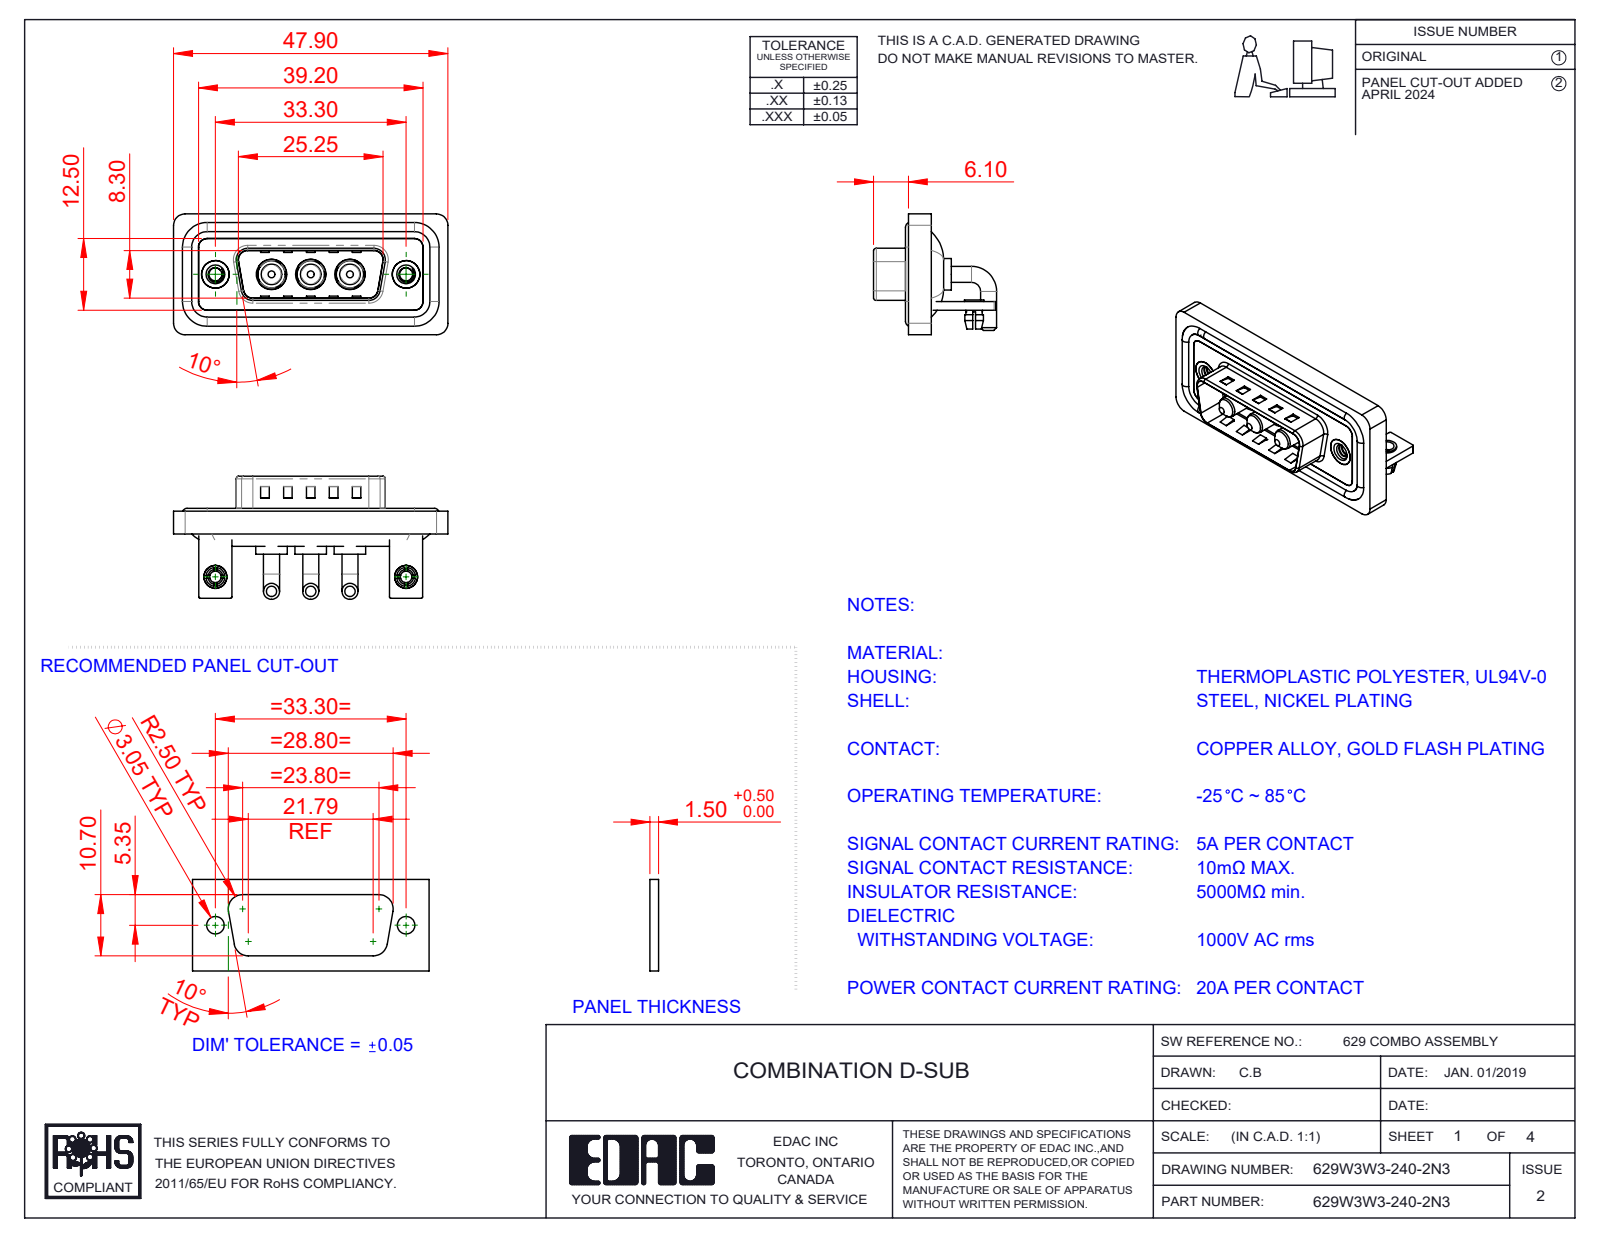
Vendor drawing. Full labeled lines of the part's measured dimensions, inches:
Part name (STEP PRODUCT): 629Combo Shell Rear_15 Contacts; 629Combo Board Lock; 629W3W3-140-2N3; 629Combo Stabilizer Bracket (+5 more)
STEP written by: SolidWorks 2023 (CONFIG_CONTROL_DESIGN)
Units: inches
Bodies: 17 solids, 708 faces (275 planar, 297 cylindrical, 136 other)
Overall size (bounding box): 1.886 × 0.846 × 0.831
Volume: 0.372 in³ · Surface area: 15.24 in²
Round holes (diameter × count): ⌀0.191 ×3, ⌀0.209 ×3, ⌀0.079 ×2, ⌀0.089 ×2, ⌀0.098 ×2, ⌀0.126 ×2, ⌀0.157 ×2, ⌀0.189 ×2, ⌀0.197 ×2
Round bosses / shafts (diameter × count): ⌀0.11 ×6, ⌀0.063 ×4, ⌀0.217 ×3, ⌀0.205 ×3, ⌀0.187 ×3, ⌀0.148 ×3, ⌀0.142 ×3, ⌀0.193 ×2
Partial cylindrical surfaces — rounded edges, fillets, slot ends (radius × count): R0.079 ×21, R0.059 ×18, R0.01 ×16, R0.02 ×9, R0.063 ×8, R0.024 ×4, R0.026 ×4, R0.035 ×4
Main face-to-face distances: 0.016, 0.059, 0.031, 0.114, 0.043, 0.083, 0.146, 0.063, 0.047, 0.177
Hole centre spacings: 0.27, 0.386, 0.656, 0.925, 1.311, 0.539
